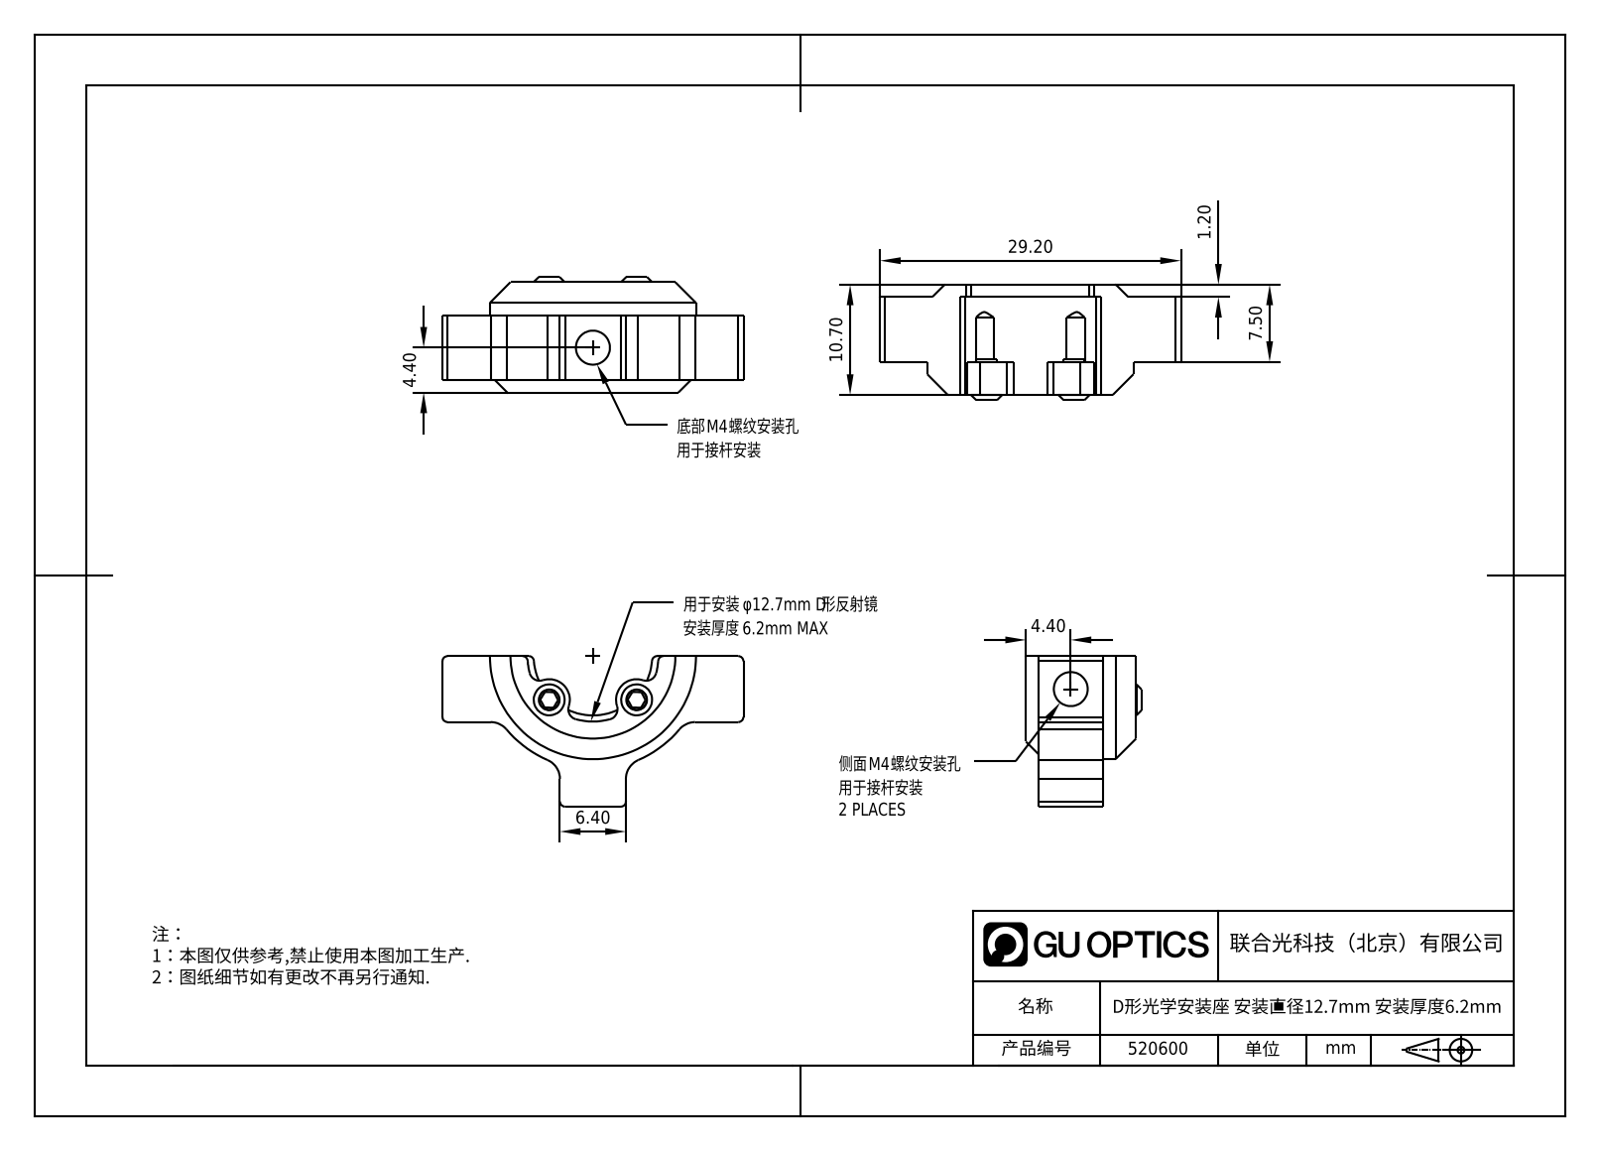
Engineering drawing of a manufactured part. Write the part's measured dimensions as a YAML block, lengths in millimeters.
part_name: "1.3.12.1_ZZM-0.5_D型安装座，用于0.5英寸D形反射镜"
step_written_by: "SolidWorks 2021 (CONFIG_CONTROL_DESIGN)"
units: millimeters
bodies: {solids: 3, faces: 102, planar: 34, cylindrical: 45, other: 23}
overall_size: [29.2, 14.6, 11.22]
volume: 1478
surface_area: 1569
round_holes:
  - {diameter: 2.5, count: 2}
  - {diameter: 3.3, count: 2}
round_bosses_or_shafts:
  - {diameter: 3, count: 2}
  - {diameter: 2, count: 2}
partial_cylinders:
  - {radius: 0.5, count: 10}
  - {radius: 2, count: 6}
  - {radius: 1, count: 4}
  - {radius: 5.75, count: 1}
  - {radius: 6.35, count: 1}
  - {radius: 10, count: 1}
  - {radius: 11, count: 1}
face_to_face_distances: [6.3, 6.4, 7.5, 1.2, 3.2, 9.5, 10.7, 11.4, 17.8, 29.2]
hole_center_spacings: [8.49]
